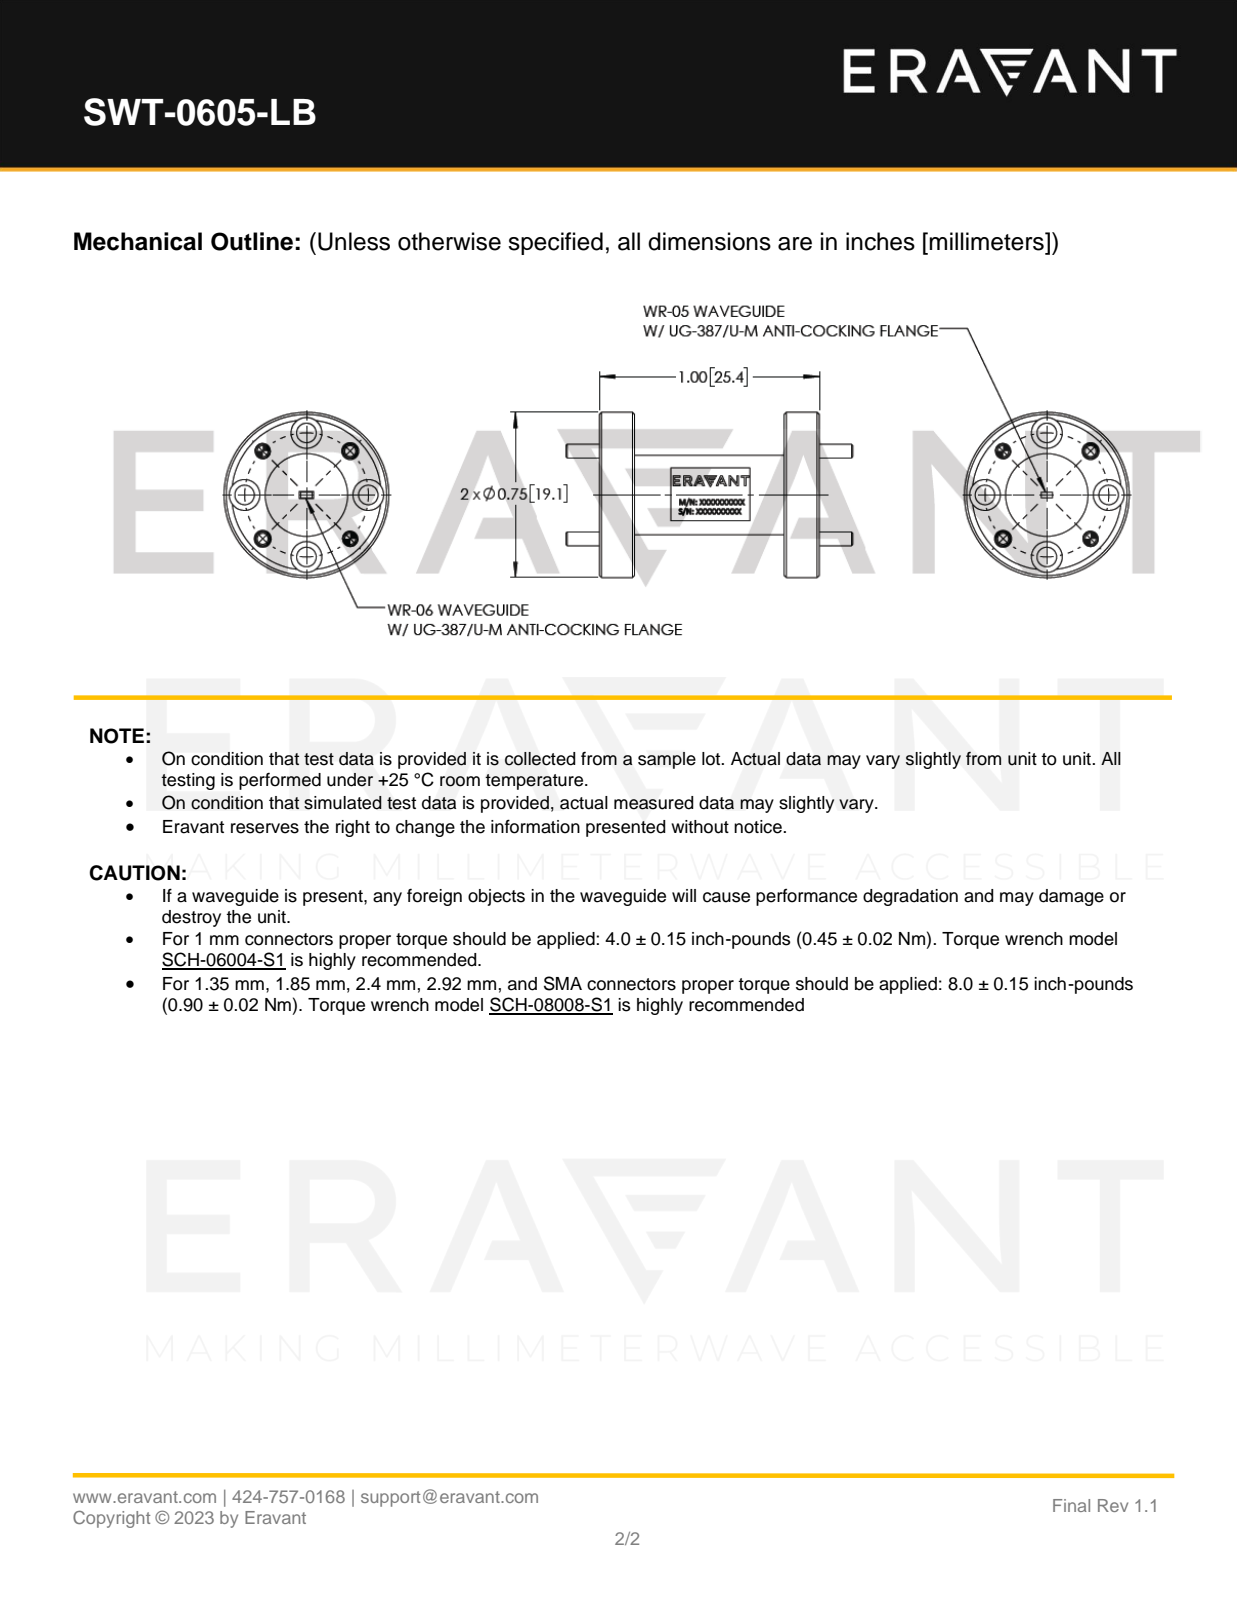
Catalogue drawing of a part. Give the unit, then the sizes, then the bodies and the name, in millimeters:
Units: millimetres
Overall size (bounding box): 33.1 × 19.1 × 19.1
Round holes (diameter × count): ⌀1.5 ×4, ⌀1.7 ×4, ⌀2.3 ×4, ⌀3.6 ×4, ⌀17.3 ×1
Round bosses / shafts (diameter × count): ⌀1.6 ×4, ⌀19.1 ×1, ⌀9.5 ×1, ⌀9.1 ×1
Main face-to-face distances: 24.9, 0.5, 17.3, 3.6, 20.8, 24.4, 20.8, 3.6, 4.1, 21.3
Hole centre spacings: 5.5, 13.2, 10.1, 7.1, 7.1, 14.3, 10.1, 5.5
Volume: 3 110 mm³ · Surface area: 2 495 mm²
Bodies: 5 solids, 148 faces (34 planar, 74 cylindrical, 40 other)
Part name (STEP PRODUCT): SWT-0605-LB
STEP written by: SolidWorks 2021 (CONFIG_CONTROL_DESIGN)
